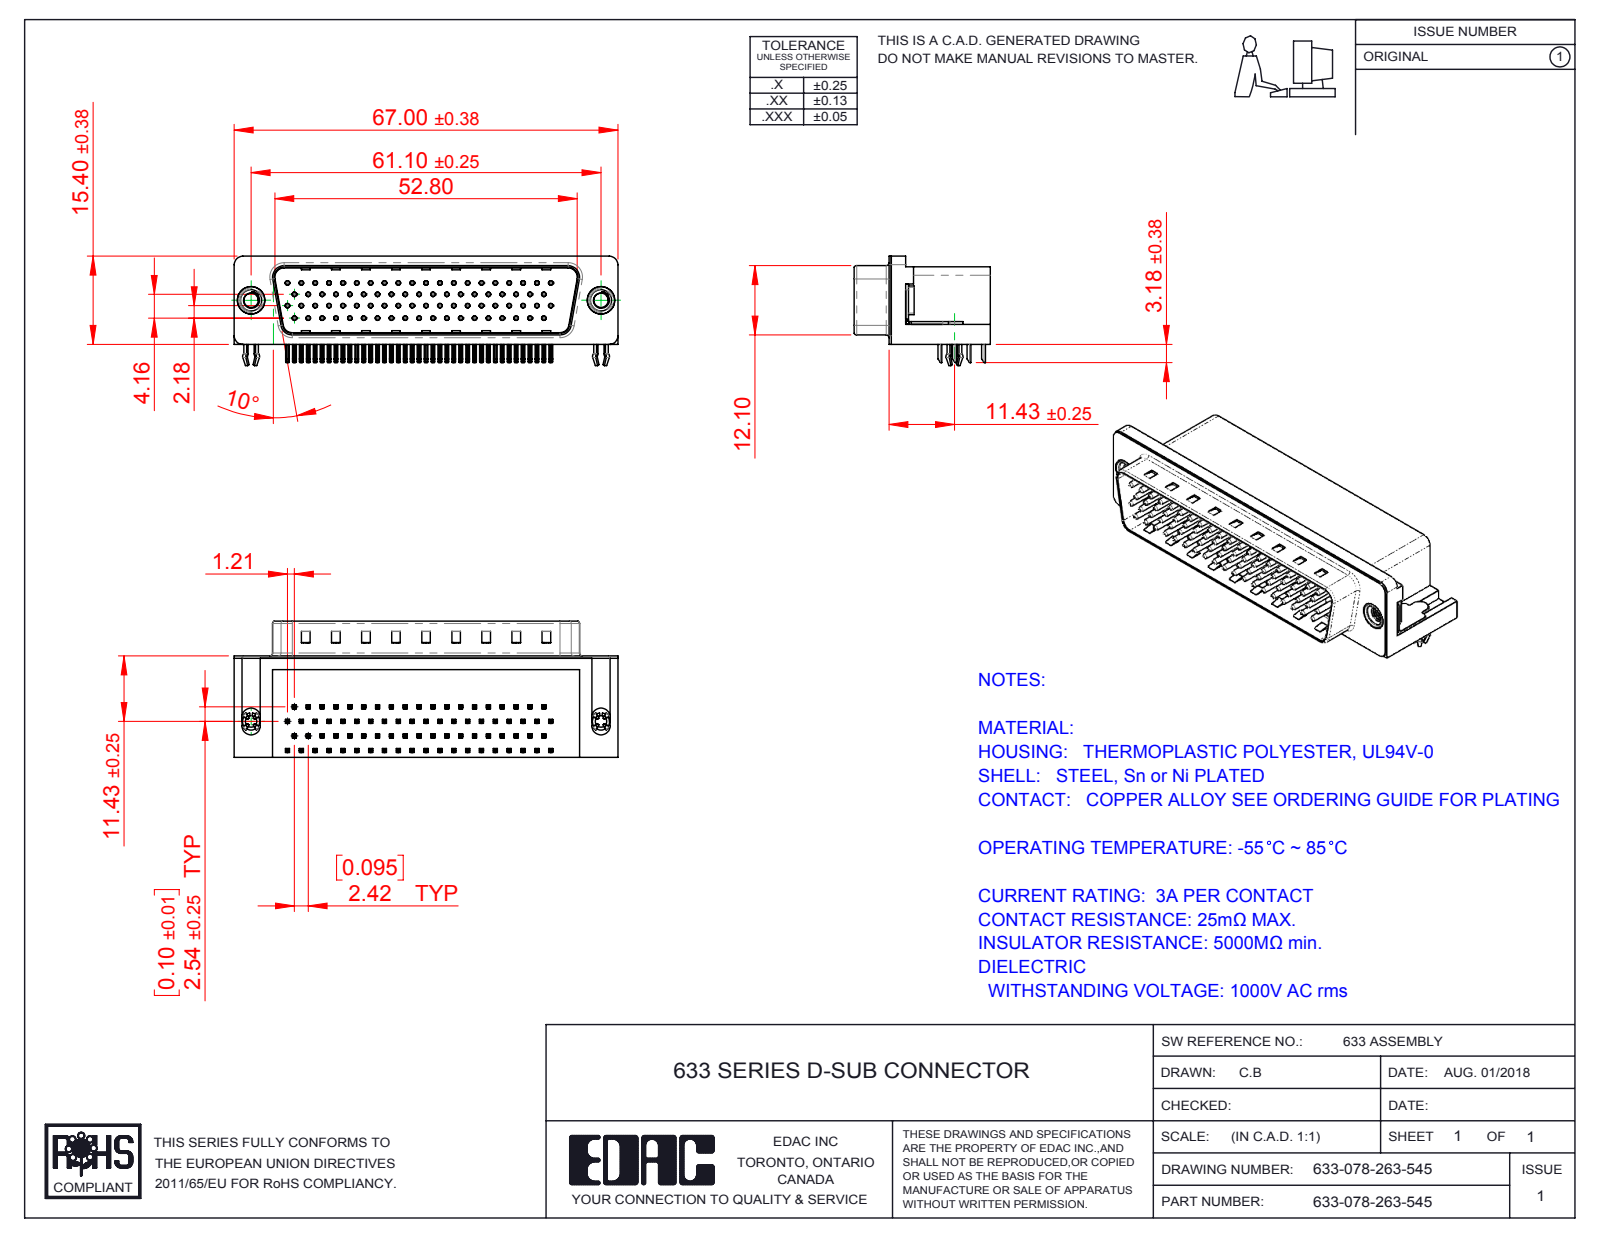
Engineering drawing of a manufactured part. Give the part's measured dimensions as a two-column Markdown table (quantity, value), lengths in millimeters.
| quantity | value |
| --- | --- |
| part name | 633-078-263-545; 633 Contact Top 78; 633 Shell_78 Contact; 633 Contact Middle_78 Contact (+5 more) |
| STEP written by | SolidWorks 2016 (CONFIG_CONTROL_DESIGN) |
| units | millimeters |
| bodies | 84 solids, 6396 faces (4023 planar, 1788 cylindrical, 585 other) |
| overall size | 67 × 23.8 × 19.1 |
| volume | 14 617 mm³ |
| surface area | 16 433 mm² |
| round holes (diameter × count) | 0.35 × 78, 0.8 × 78, 2 × 2, 2.5 × 2, 4 × 2, 4.8 × 2, 5 × 2 |
| round bosses / shafts (diameter × count) | 0.75 × 78, 4.9 × 2, 4.75 × 2, 3.9 × 2, 3 × 2 |
| partial cylindrical surfaces (radius × count) | 0.25 × 324, 0.12 × 156, 1 × 16, 0.5 × 9, 1.6 × 8, 1.5 × 6, 0.45 × 4, 0.9 × 4 |
| main face-to-face distances | 0.4, 13.2, 17.3, 11.7, 13.35, 2.05, 13.75, 1.65, 1.85, 11.9 |
| hole center spacings | 2.42, 4.84, 7.26, 9.68, 6.26, 7.13, 12.1, 8.62 |
